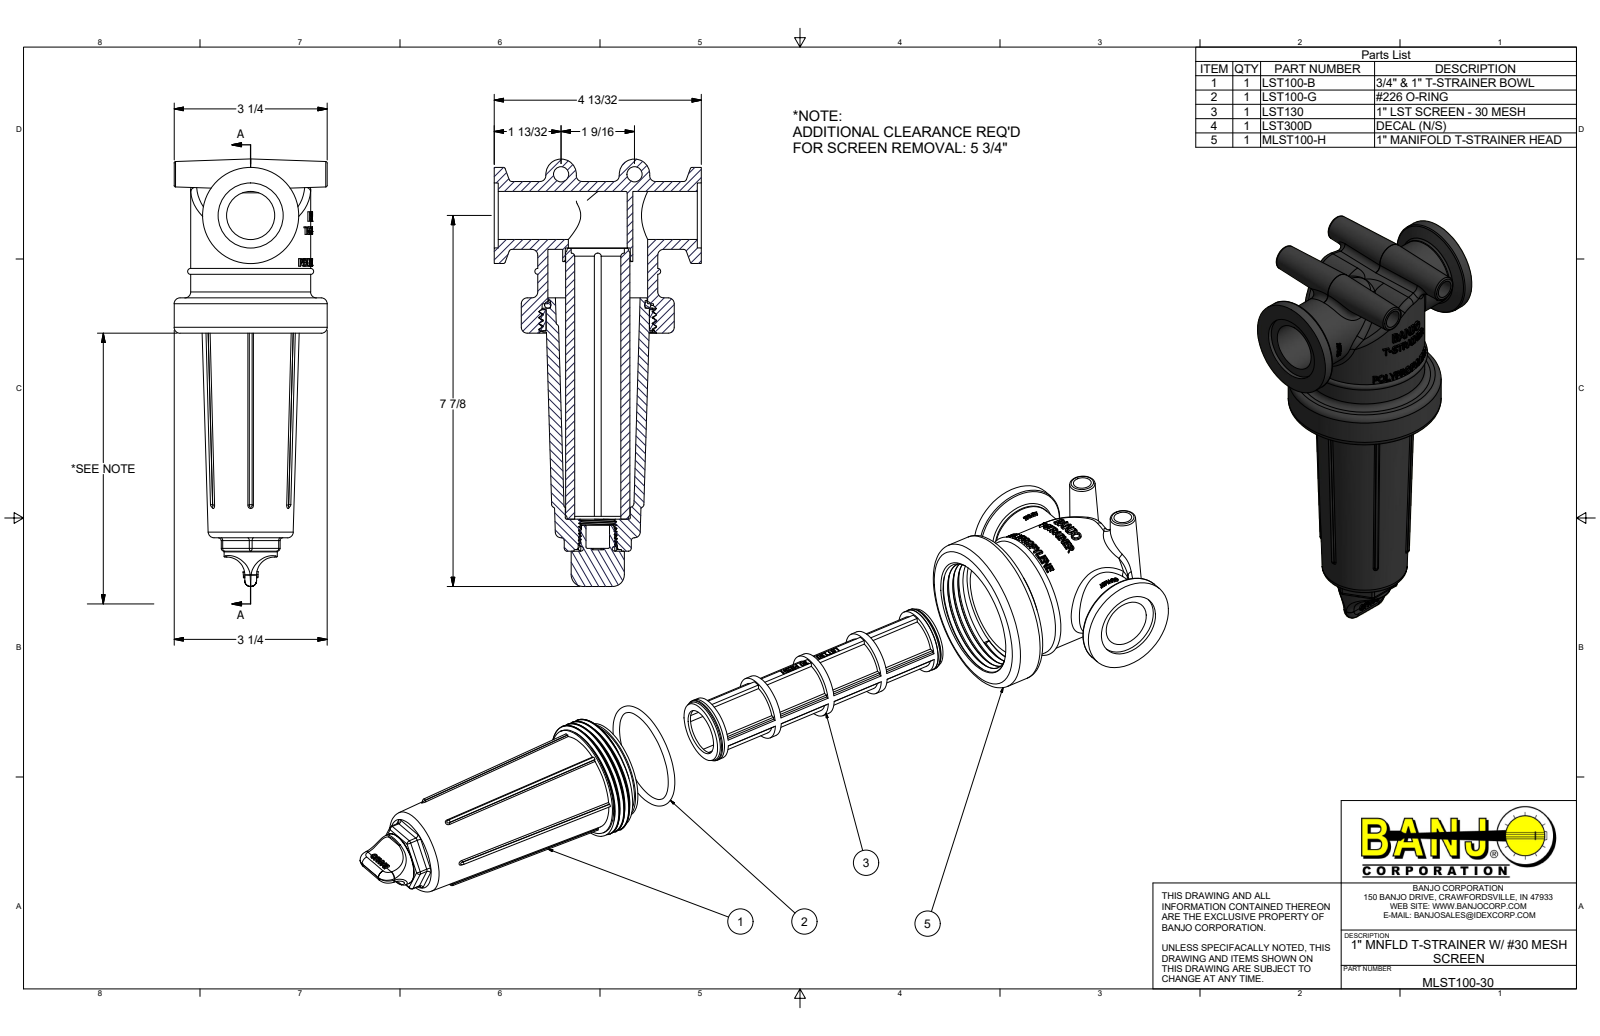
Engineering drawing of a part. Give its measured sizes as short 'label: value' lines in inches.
name: MLST100-H; LST100-XB; 12777; UV15163 (+4 more)
written by: Autodesk Inventor 2014 (AUTOMOTIVE_DESIGN)
unit: in
bodies: 7 solids, 1358 faces (678 planar, 171 cylindrical, 509 other)
size: 9.08 × 4.4 × 3.25
volume: 18.91 in³; area: 252.1 in²
holes: 2× ⌀1.38, 1× ⌀0.5, 1× ⌀0.98, 1× ⌀1.005, 1× ⌀1.02, 1× ⌀1.1, 1× ⌀1.25, 1× ⌀2.12, 1× ⌀2.194, 1× ⌀2.365
bosses: 1× ⌀3.25, 1× ⌀2.55, 1× ⌀2.5, 1× ⌀2.34, 1× ⌀2.1, 1× ⌀2.04, 1× ⌀2.01, 1× ⌀1.49
rounds: 19× R0.06, 9× R0.03, 4× R0.075, 2× R0.35, 2× R0.38, 1× R0.224, 1× R0.5, 1× R0.75
face distances: 0.15, 1.35, 0.05, 0.03, 0.48, 0.75, 0.25, 1.2, 1.5, 4.4
